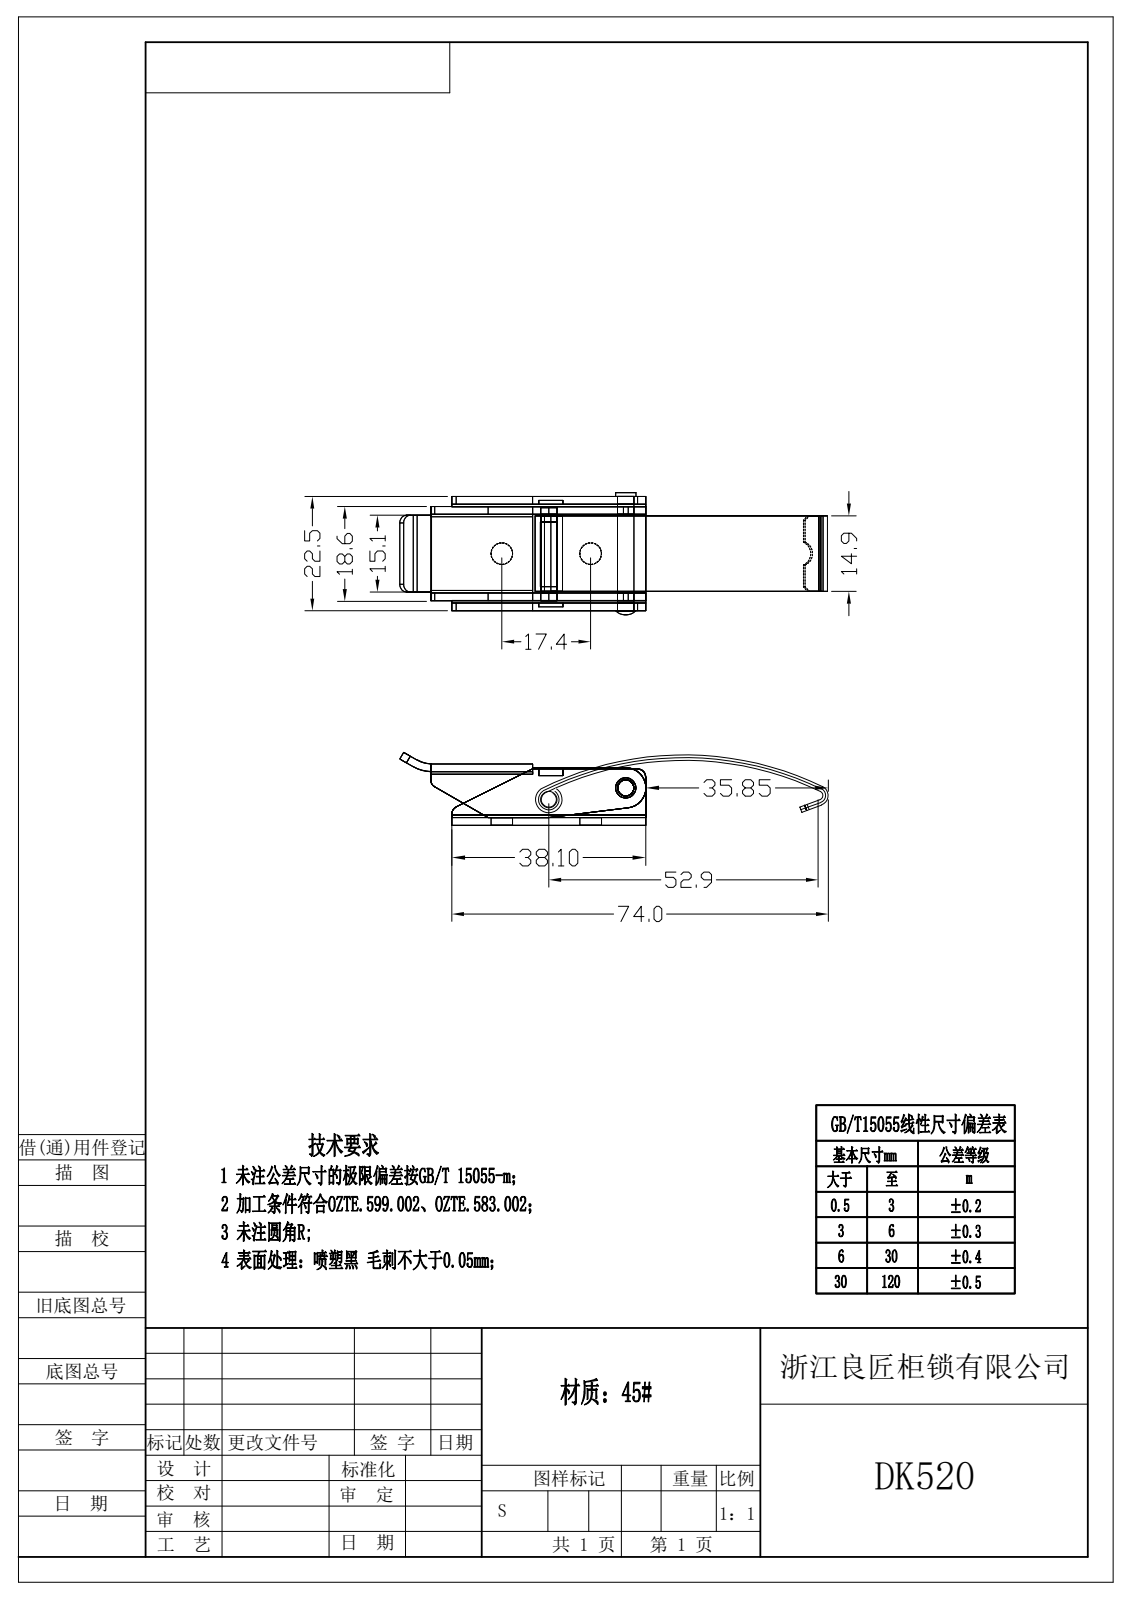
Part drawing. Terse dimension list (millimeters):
written by: Rhino 8.5 (CONFIG_CONTROL_DESIGN)
unit: mm
bodies: 5 solids, 117 faces (61 planar, 45 cylindrical, 11 other)
size: 84.77 × 25.46 × 14.32
volume: 5 172 mm³; area: 8 464 mm²
holes: 2× ⌀3.2, 2× ⌀4.24, 1× ⌀3.15, 1× ⌀3.23
bosses: 2× ⌀3, 1× ⌀3.5
rounds: 4× R0.5, 2× R1.5, 2× R1.59, 2× R2, 1× R1.52, 1× R3.96, 1× R5.59, 1× R7.11
face distances: 1.52, 10.52, 1.5, 17, 12.04, 18.5, 15.5, 9, 3.5, 1.98
hole spacings: 15.26, 17.45
